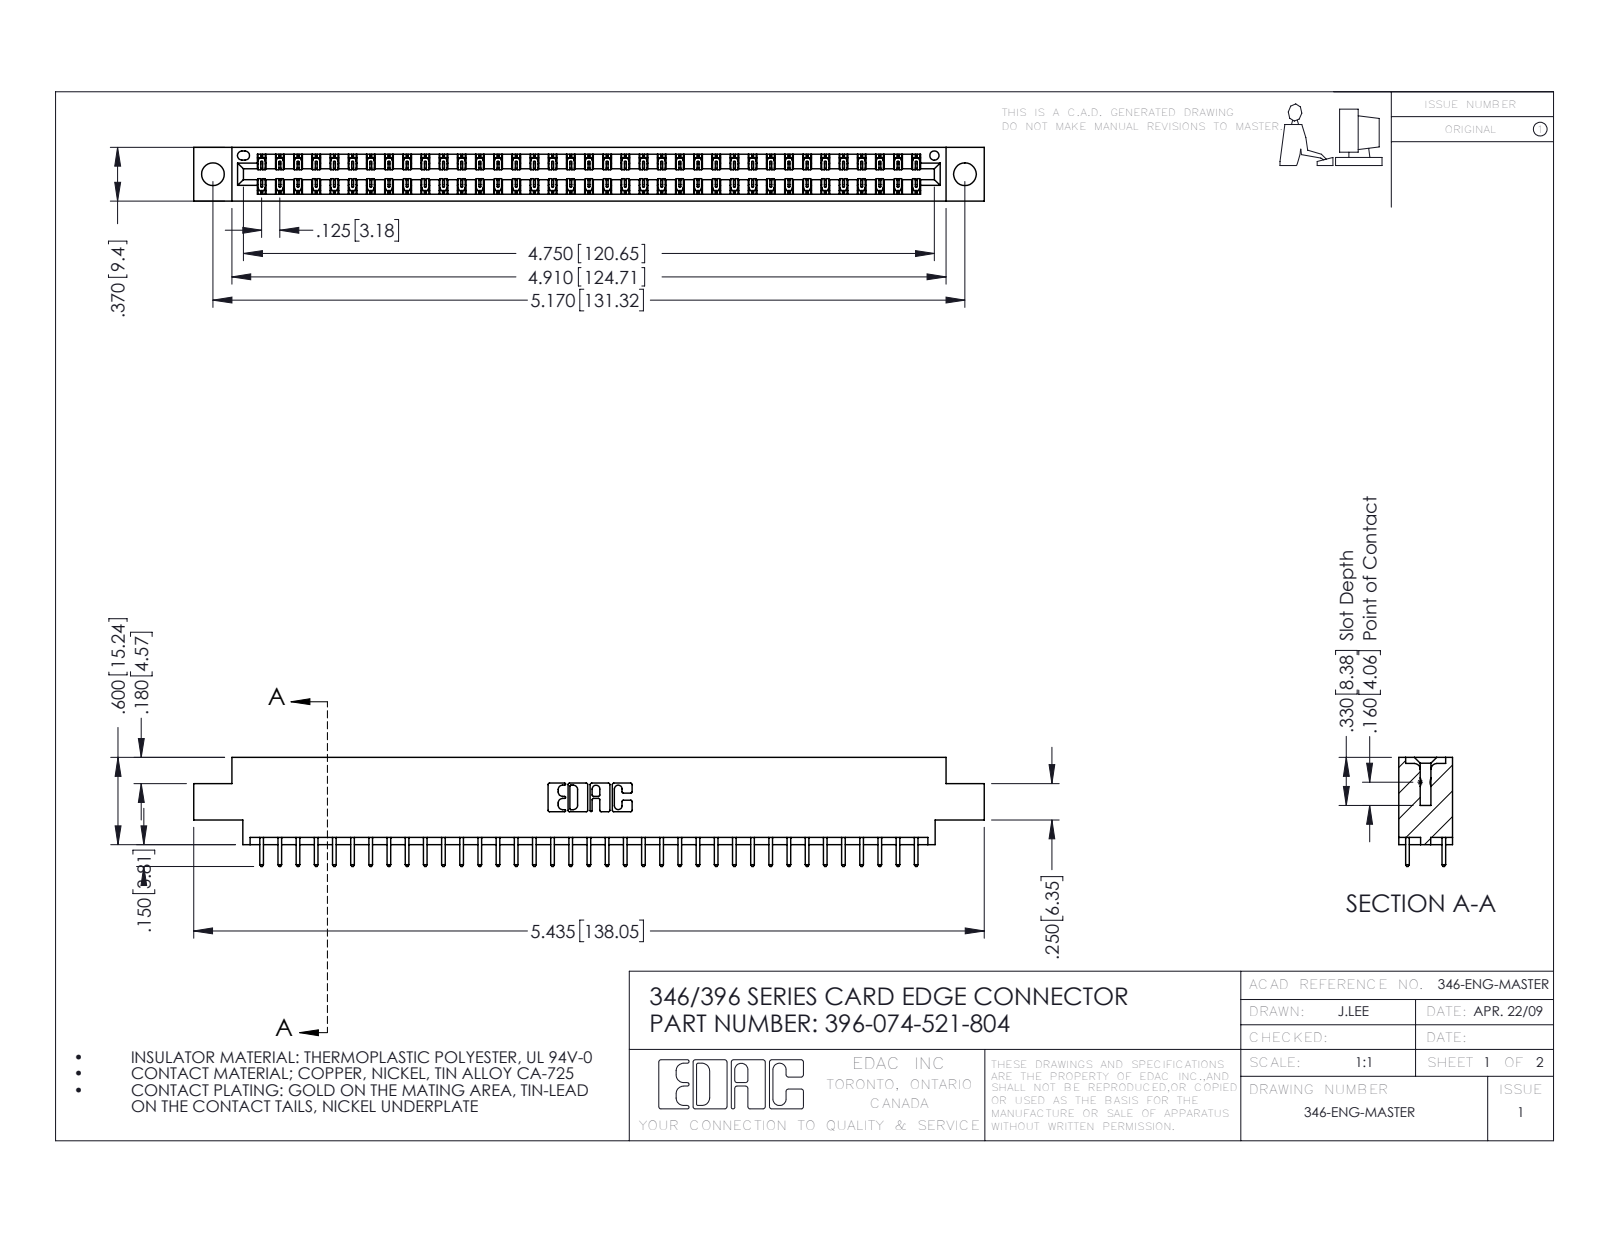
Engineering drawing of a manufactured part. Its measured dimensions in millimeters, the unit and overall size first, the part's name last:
Units: millimetres
Overall size (bounding box): 138 × 19.1 × 9.4
Round holes (diameter × count): ⌀4 ×2, ⌀1.6 ×1
Partial cylindrical surfaces — rounded edges, fillets, slot ends (radius × count): R0.2 ×111, R0.3 ×74, R0.3 ×22, R0.2 ×6, R0.8 ×6, R0.7 ×3, R0.4 ×2, R0.6 ×2
Main face-to-face distances: 1.2, 8.2, 9.4, 6.4, 1.8, 7.6, 0.6, 7, 3.8, 5.6
Hole centre spacings: 6.2, 126, 131.3
Volume: 13 100 mm³ · Surface area: 17 790 mm²
Bodies: 75 solids, 3974 faces (2670 planar, 1304 cylindrical, 0 other)
Part name (STEP PRODUCT): 346 Part_0.170 Offset - 0.156 Dia-TH; 345-292-001_345-293-121; 396-074-521-804
STEP written by: SolidWorks 2016 (CONFIG_CONTROL_DESIGN)
